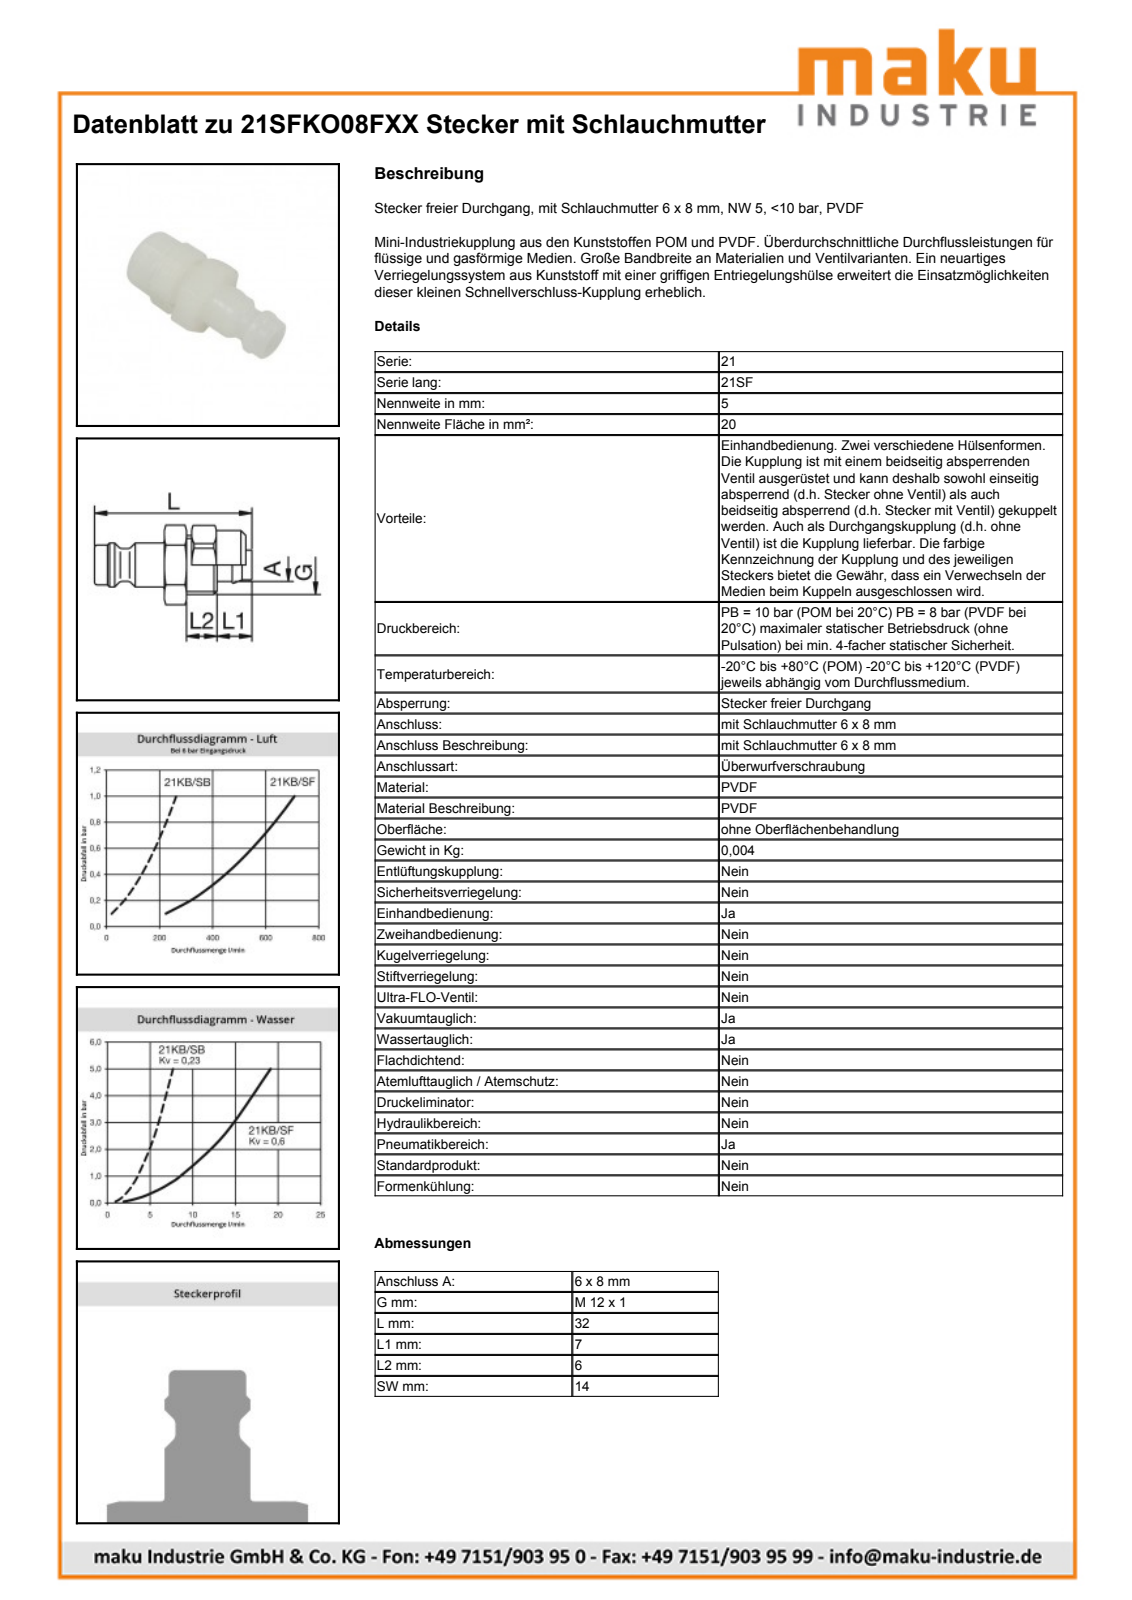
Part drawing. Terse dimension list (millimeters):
name: D108456; D108452; D105558
written by: Autodesk Inventor 2013 (AUTOMOTIVE_DESIGN)
unit: mm
bodies: 2 solids, 88 faces (20 planar, 25 cylindrical, 43 other)
size: 32 × 15.8 × 14.01
volume: 2 388 mm³; area: 2 834 mm²
holes: 1× ⌀4.95, 1× ⌀8.25, 1× ⌀12, 1× ⌀12.5
bosses: 1× ⌀14, 1× ⌀10.4, 1× ⌀9, 1× ⌀8.1, 1× ⌀6.7, 1× ⌀6.65, 1× ⌀6.05
rounds: 1× R7.75, 1× R7.9
face distances: 14, 4.65, 10.8, 6.15, 15.65, 11, 4.85, 14.1, 18.75, 24.9
